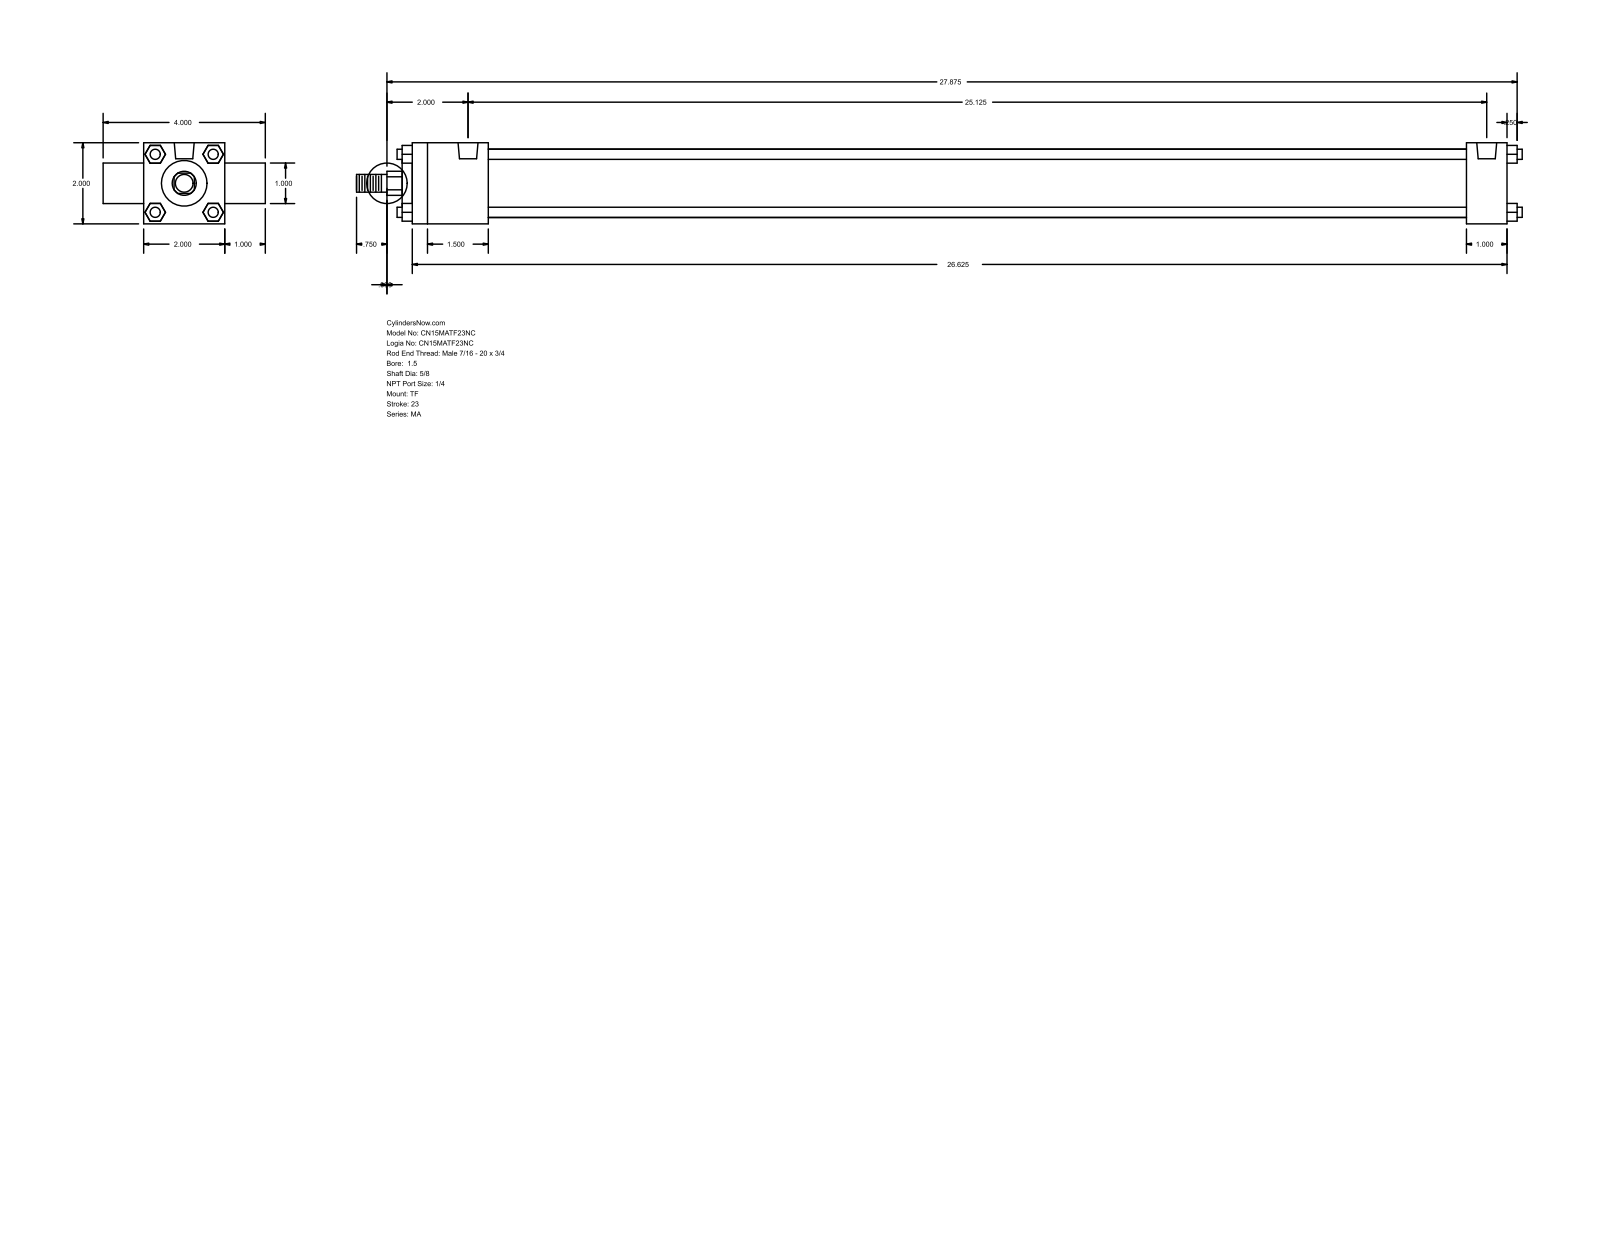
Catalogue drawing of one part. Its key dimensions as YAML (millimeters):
part_name: "MA_TF__0150_0.625"
step_written_by: "GSSL Pune (CONFIG_CONTROL_DESIGN)"
units: millimeters
bodies: {solids: 0, faces: 120, planar: 92, cylindrical: 28, other: 0}
overall_size: [730.25, 101.6, 50.8]
round_holes:
  - {diameter: 7.94, count: 3}
  - {diameter: 12.49, count: 2}
round_bosses_or_shafts:
  - {diameter: 6.35, count: 4}
  - {diameter: 42.93, count: 1}
  - {diameter: 28.57, count: 1}
  - {diameter: 25.4, count: 1}
  - {diameter: 15.88, count: 1}
  - {diameter: 11.11, count: 1}
partial_cylinders:
  - {radius: 7.54, count: 1}
face_to_face_distances: [50.8, 25.4, 685.79, 6.35, 692.14, 76.2, 47.62, 660.39, 612.77, 638.17]
hole_center_spacings: [638.18]
